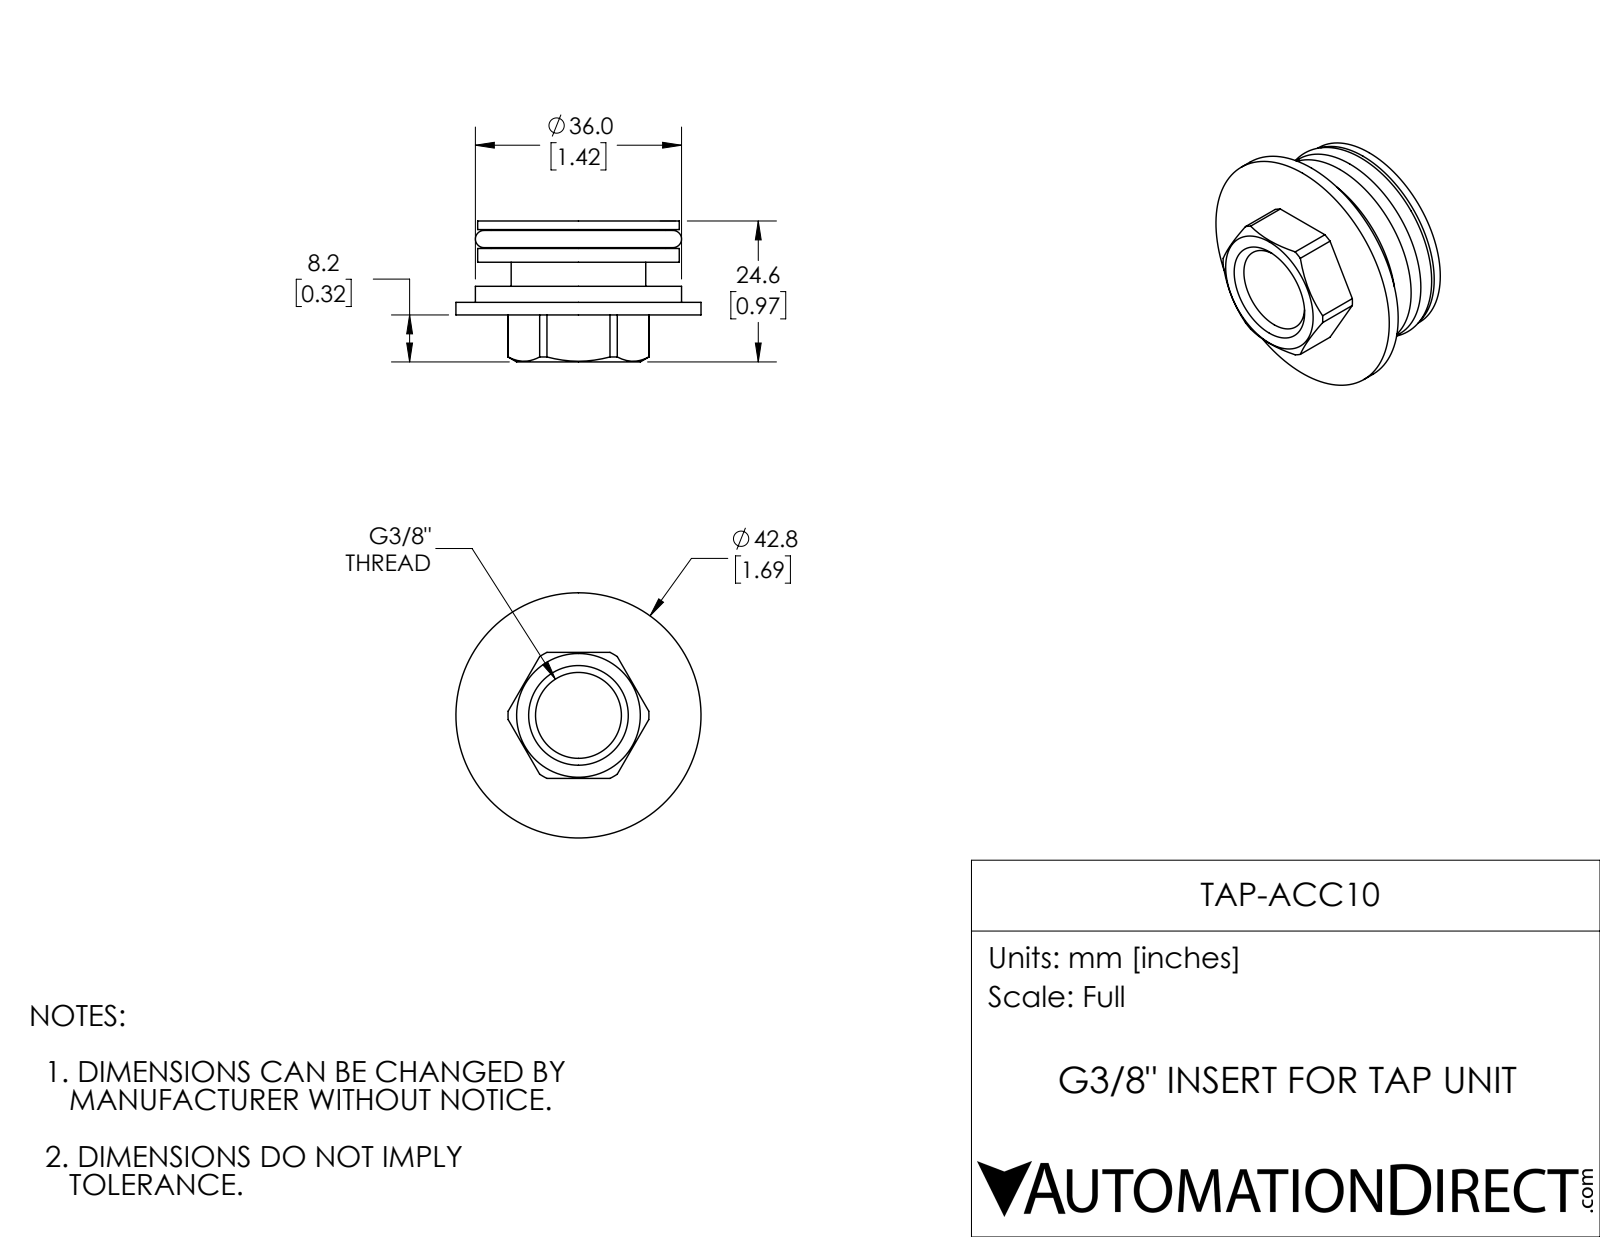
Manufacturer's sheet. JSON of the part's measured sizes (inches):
{"part_name": "TAP-ACC10", "step_written_by": "SolidWorks 2017 (AUTOMOTIVE_DESIGN)", "units": "inches", "bodies": {"solids": 1, "faces": 48, "planar": 14, "cylindrical": 24, "other": 10}, "overall_size": [1.685, 1.685, 0.969], "volume_in3": 0.743, "surface_area_in2": 12.53, "round_holes": [[0.591, 1], [1.024, 1]], "round_bosses_or_shafts": [[1.685, 1], [1.417, 1], [1.386, 1], [1.201, 1], [0.925, 1]], "partial_cylinders_radius": [[0.484, 1]], "face_to_face_distances": [0.197, 0.362, 0.165, 0.646, 0.449, 0.283, 0.087, 0.11, 0.276, 0.559]}
